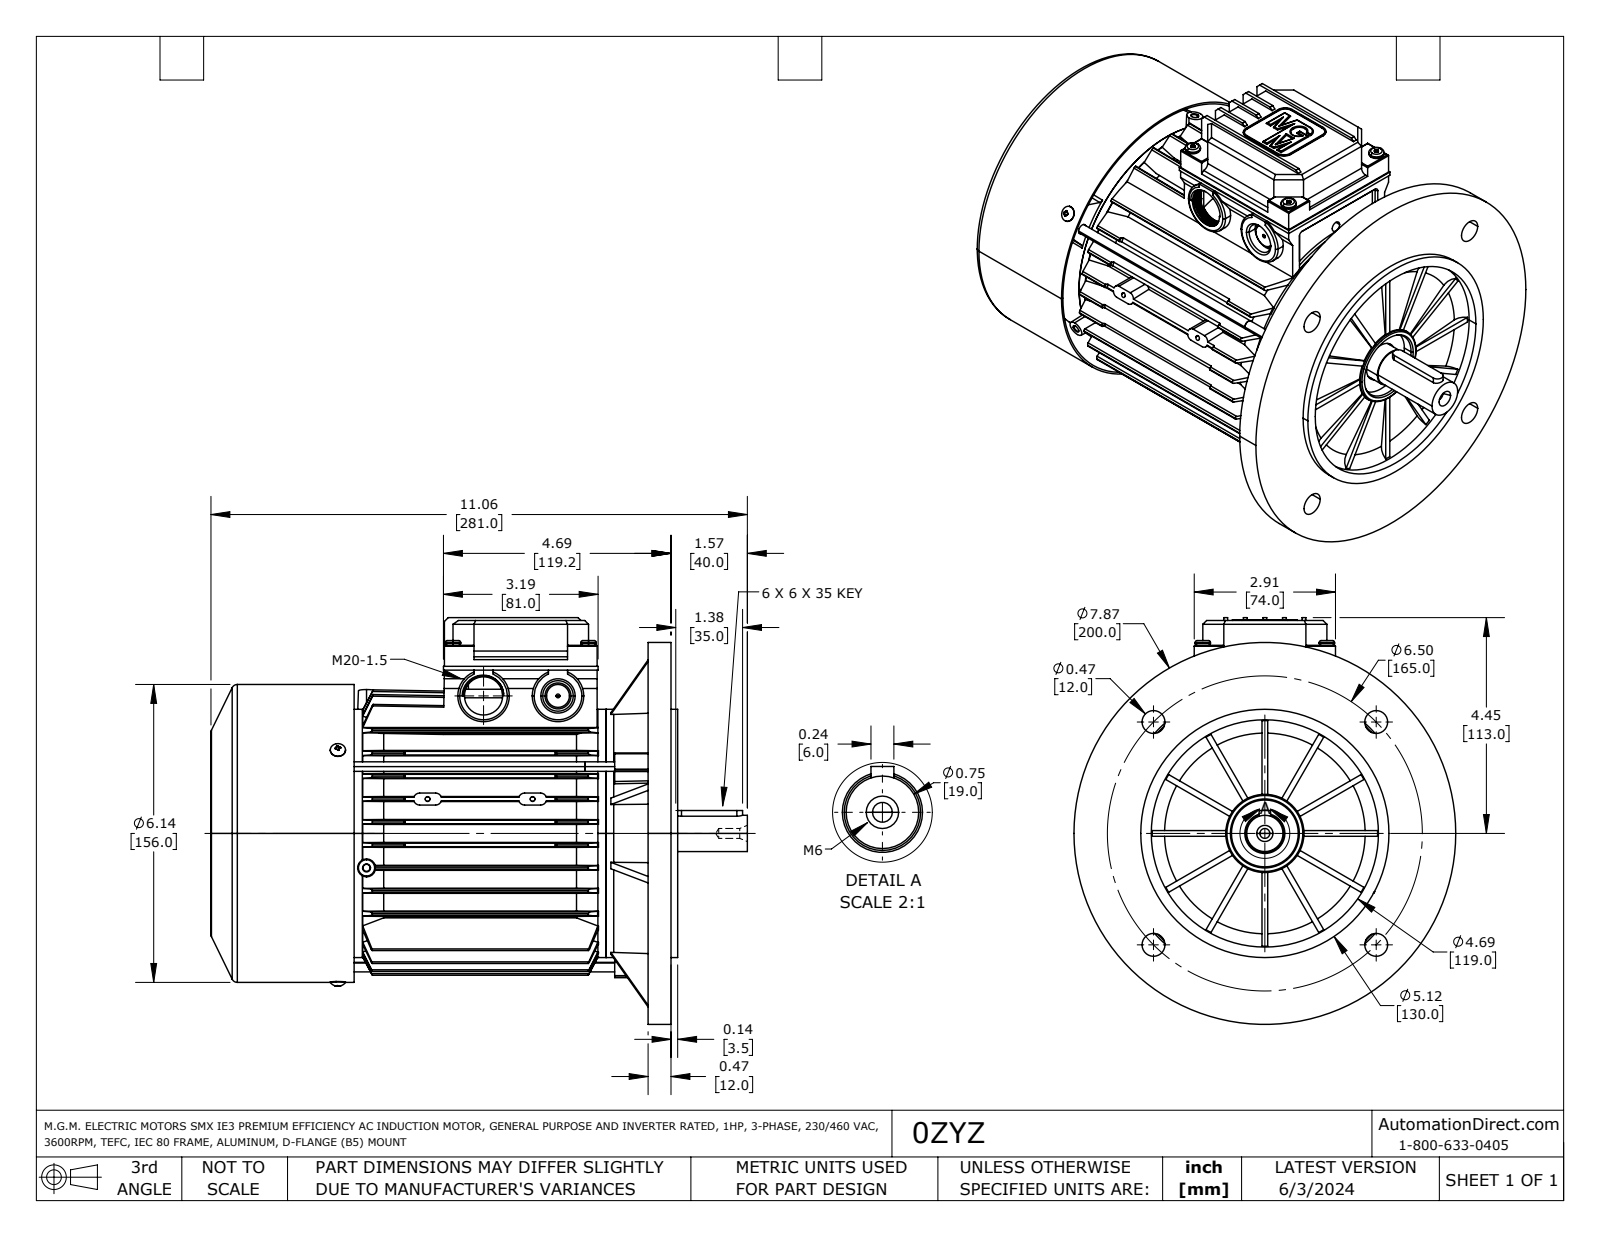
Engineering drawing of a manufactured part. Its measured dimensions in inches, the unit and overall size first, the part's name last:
Units: inches
Overall size (bounding box): 11.063 × 8.386 × 7.874
Round holes (diameter × count): ⌀0.118 ×12, ⌀0.146 ×8, ⌀0.217 ×8, ⌀0.157 ×4, ⌀0.472 ×4, ⌀0.126 ×3, ⌀0.165 ×3, ⌀0.177 ×3, ⌀0.276 ×3, ⌀0.205 ×1, ⌀0.315 ×1, ⌀0.63 ×1
Round bosses / shafts (diameter × count): ⌀0.118 ×10, ⌀0.315 ×7, ⌀0.138 ×4, ⌀1.063 ×3, ⌀0.197 ×3, ⌀0.079 ×3, ⌀0.248 ×2, ⌀7.874 ×1
Partial cylindrical surfaces — rounded edges, fillets, slot ends (radius × count): R0.039 ×266, R0.016 ×36, R0.008 ×32, R0.02 ×30, R0.035 ×30, R0.004 ×16, R0.033 ×16, R0.197 ×9
Main face-to-face distances: 0.256, 0.079, 3.304, 0.217, 0.463, 2.841, 2.822, 0.481, 2.36, 0.929
Hole centre spacings: 0.478, 2.756, 0.571, 0.748, 1.102, 1.22, 1.222, 1.559
Volume: 53.11 in³ · Surface area: 868.6 in²
Bodies: 21 solids, 2867 faces (1080 planar, 963 cylindrical, 824 other)
Part name (STEP PRODUCT): 0ZYZ
STEP written by: SolidWorks 2021 (AUTOMOTIVE_DESIGN)
